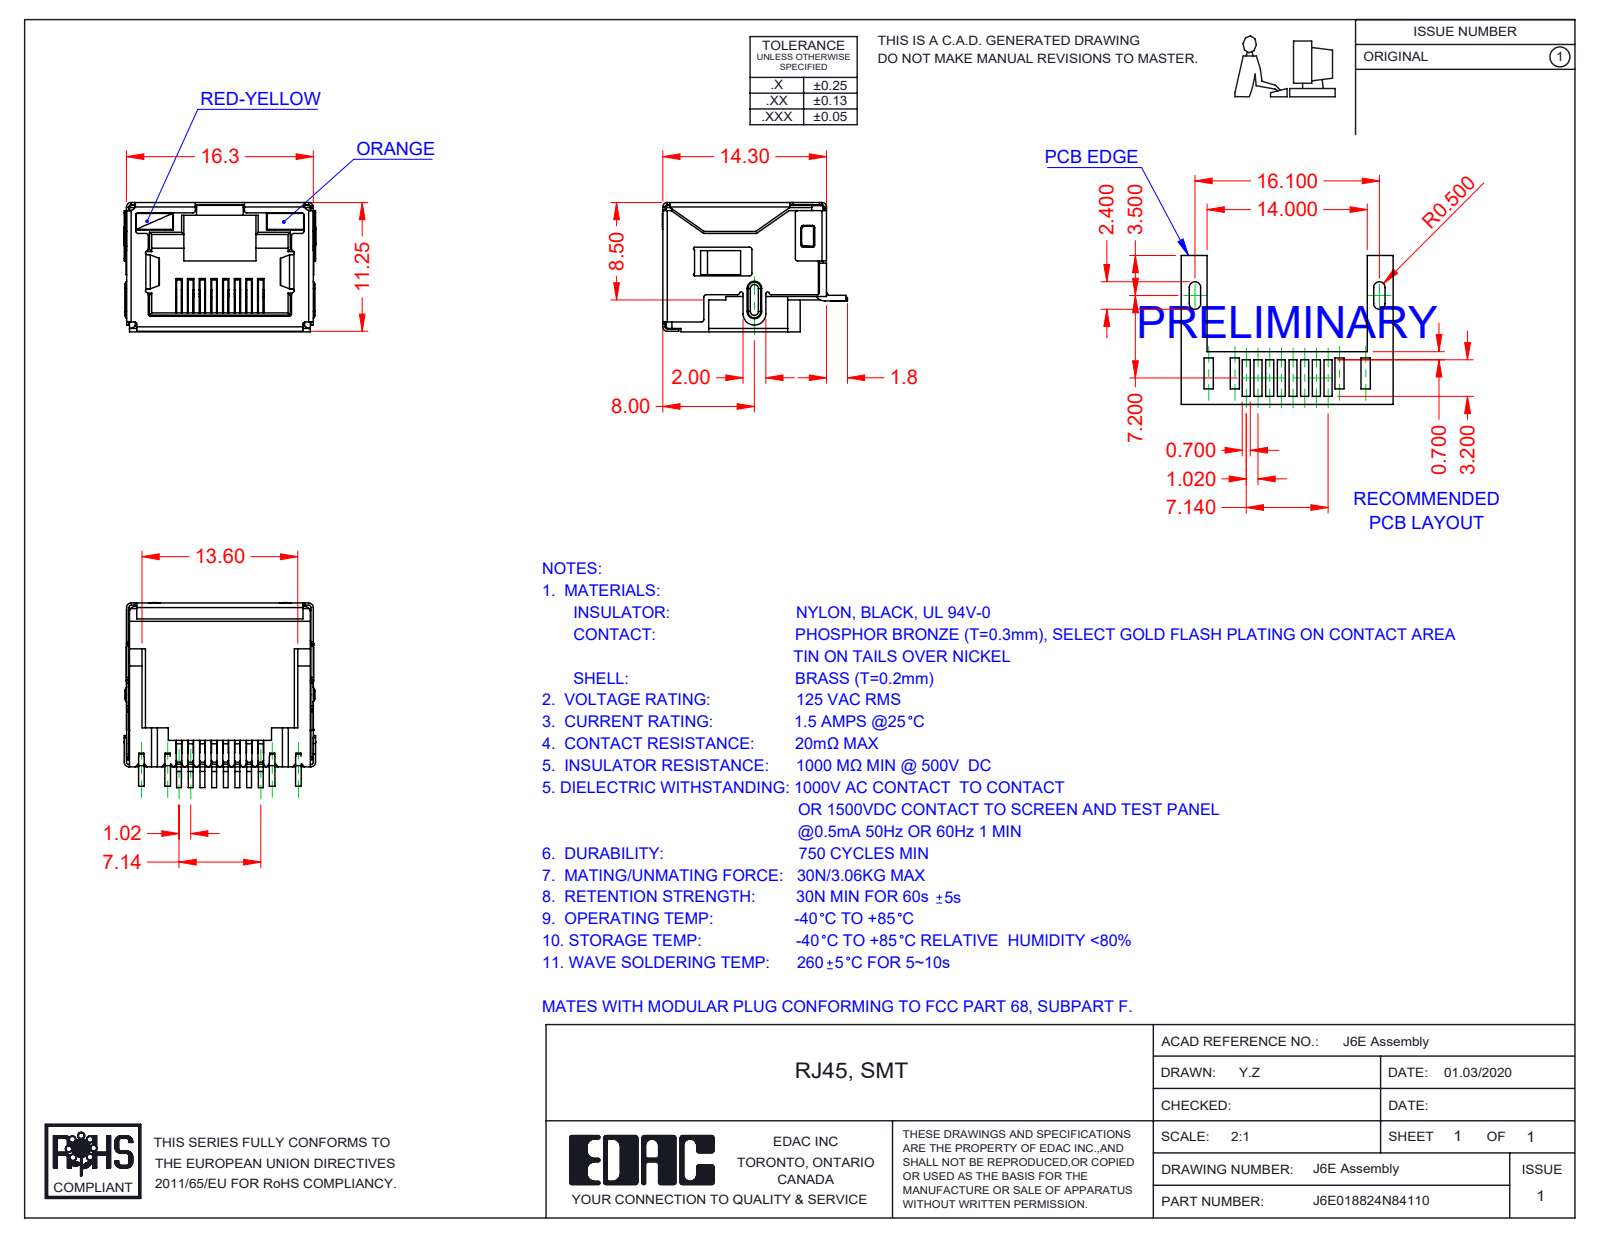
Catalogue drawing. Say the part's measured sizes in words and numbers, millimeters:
The part is named "6E LED RH_4-Orange; J6E018824N84110; 6E Contacts; 6E LED LH_8-Red-Yellow (+2 more)". Its 3-D file was written by "SolidWorks 2016 (CONFIG_CONTROL_DESIGN)". It is 12 solids with 1498 faces: 1099 planar, 349 cylindrical and 50 other. Overall it measures 16.75 by 16.15 by 11.3 millimeters. Its volume is 1 109 cubic millimeters and its surface area 4 045 square millimeters. Partial cylindrical surfaces (rounded edges, fillets, slot ends): 82 of radius 0.2, 17 of radius 0.25, 13 of radius 0.4, 13 of radius 0.5, 10 of radius 0.1, 7 of radius 0.15, 4 of radius 0.3, 3 of radius 1. The main face-to-face distances are 11.05, 16.05, 16.1, 15.85, 11.1, 11.3, 2.4, 0.7, 9.85, 0.49.
